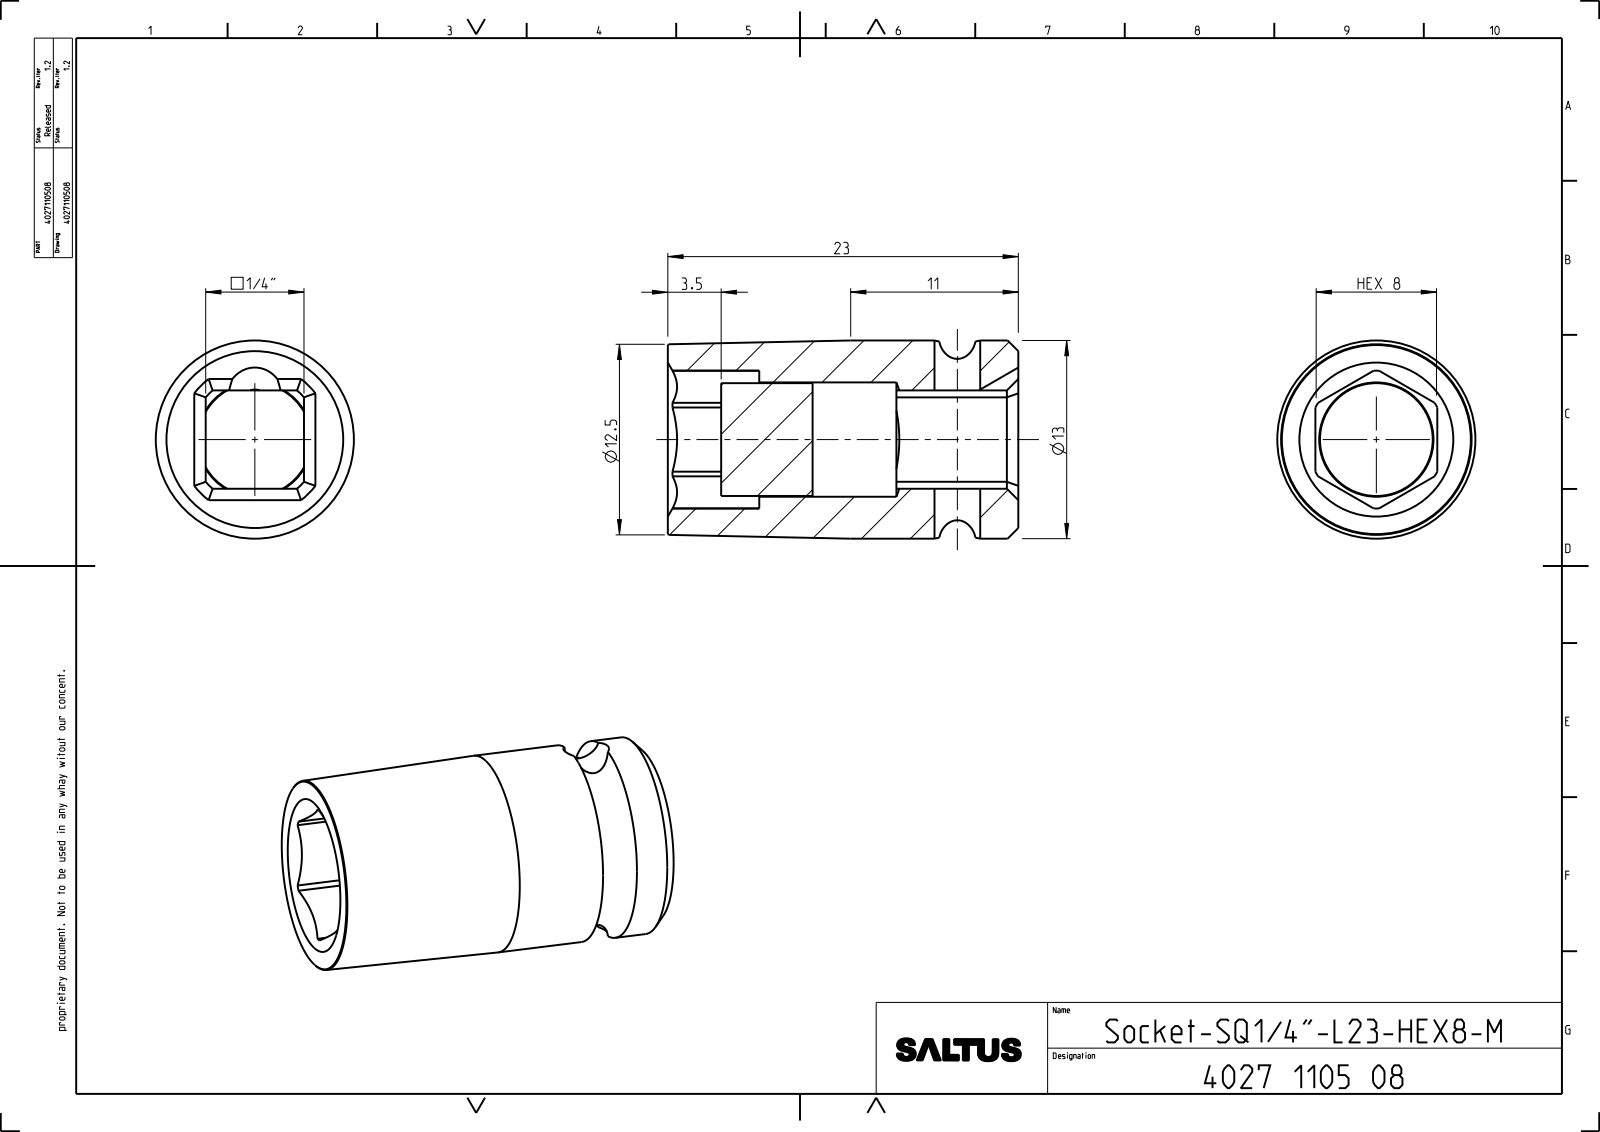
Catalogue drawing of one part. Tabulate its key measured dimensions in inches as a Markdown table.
| quantity | value |
| --- | --- |
| part name | 4027110508 |
| STEP written by | CREO PARAMETRIC BY PTC INC, 2022414 (CONFIG_CONTROL_DESIGN) |
| units | inches |
| bodies | 2 solids, 65 faces (24 planar, 23 cylindrical, 18 other) |
| overall size | 0.906 × 0.512 × 0.512 |
| volume | 0.126 in³ |
| surface area | 2.967 in² |
| round holes (diameter × count) | 0.118 × 1, 0.295 × 1 |
| round bosses / shafts (diameter × count) | 0.512 × 1, 0.291 × 1 |
| partial cylindrical surfaces (radius × count) | 0.079 × 1, 0.167 × 1, 0.178 × 1 |
| main face-to-face distances | 0.315, 0.254, 0.236, 0.138, 0.03, 0.285, 0.531, 0.768, 0.906, 0.374 |
